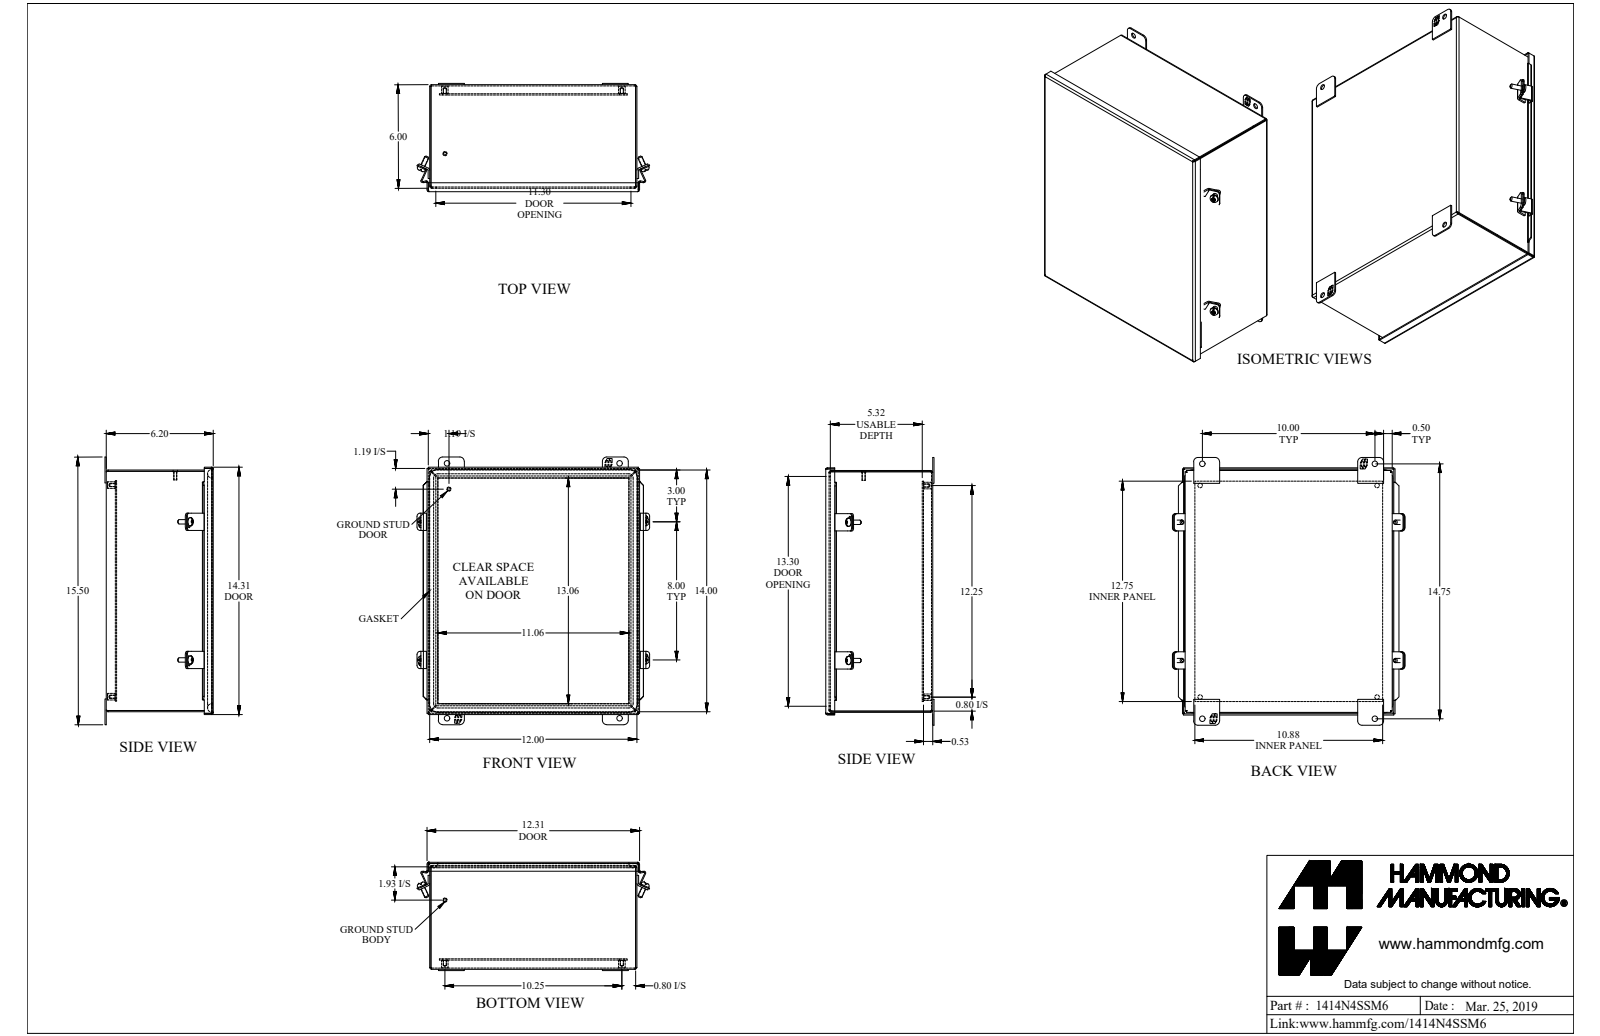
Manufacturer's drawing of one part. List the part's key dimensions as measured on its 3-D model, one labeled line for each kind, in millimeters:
Part name (STEP PRODUCT): 1414N4SSM6
STEP written by: SolidWorks 2018 (AUTOMOTIVE_DESIGN)
Units: millimetres
Bodies: 26 solids, 720 faces (476 planar, 168 cylindrical, 76 other)
Overall size (bounding box): 393.7 × 342.3 × 159.2
Volume: 1 084 000 mm³ · Surface area: 1 185 000 mm²
Round holes (diameter × count): ⌀4 ×4, ⌀5.4 ×4, ⌀6.7 ×4, ⌀8 ×4
Round bosses / shafts (diameter × count): ⌀6.4 ×6, ⌀12.2 ×4, ⌀9.5 ×4, ⌀4.8 ×2
Partial cylindrical surfaces — rounded edges, fillets, slot ends (radius × count): R6.4 ×24, R4.8 ×16, R0.9 ×10, R2.7 ×10, R3.6 ×8, R0.2 ×4, R0.3 ×4, R0.7 ×4
Main face-to-face distances: 1.8, 13.5, 1.8, 155.6, 157.4, 155.6, 153.7, 303, 15.3, 143.9
Hole centre spacings: 259.1, 405.7, 31.9, 342.9, 260.4, 260.4, 311.2, 311.2
